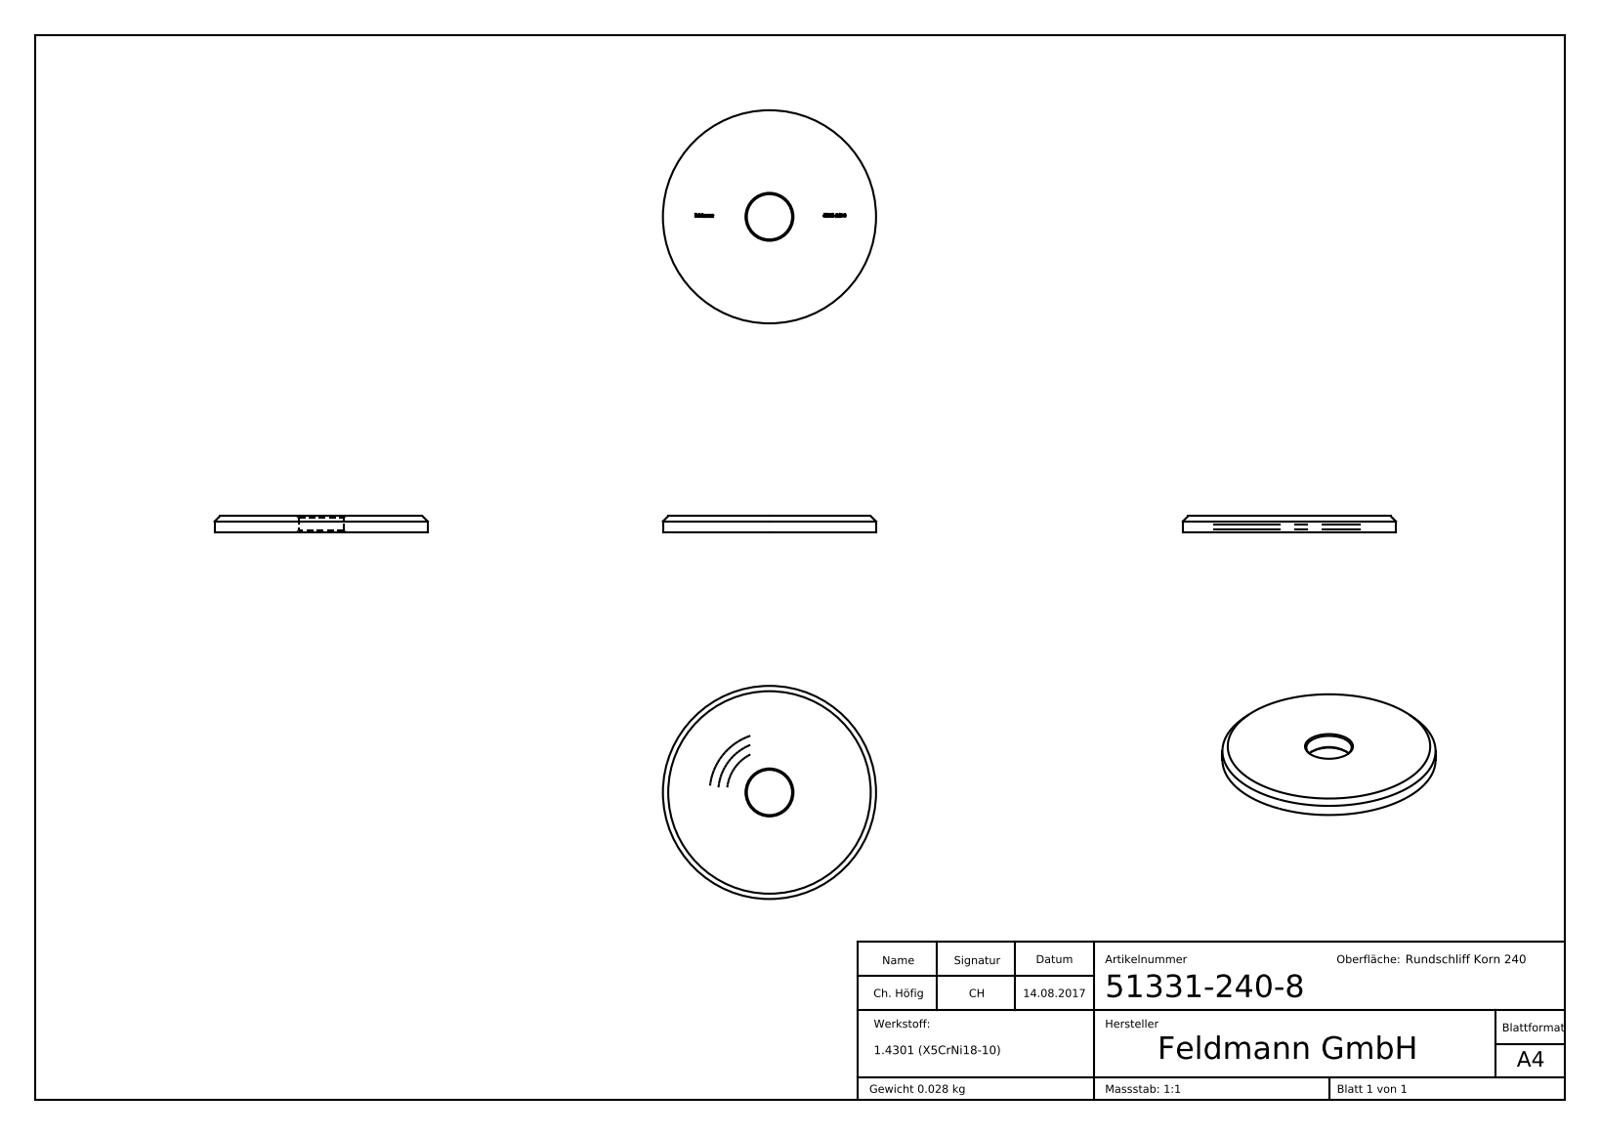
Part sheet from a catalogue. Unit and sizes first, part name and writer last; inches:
Units: inches
Overall size (bounding box): 1.575 × 1.575 × 0.118
Round holes (diameter × count): ⌀0.335 ×1
Round bosses / shafts (diameter × count): ⌀1.575 ×1
Main face-to-face distances: 0.118, 0.114, 0.047, 0.942, 0.014, 1.022, 0.021, 0.969, 1.035, 0.093
Volume: 0.216 in³ · Surface area: 4.306 in²
Bodies: 1 solid, 259 faces (133 planar, 4 cylindrical, 122 other)
Part name (STEP PRODUCT): 51331-240-8
STEP written by: SolidWorks 2018 (CONFIG_CONTROL_DESIGN)
